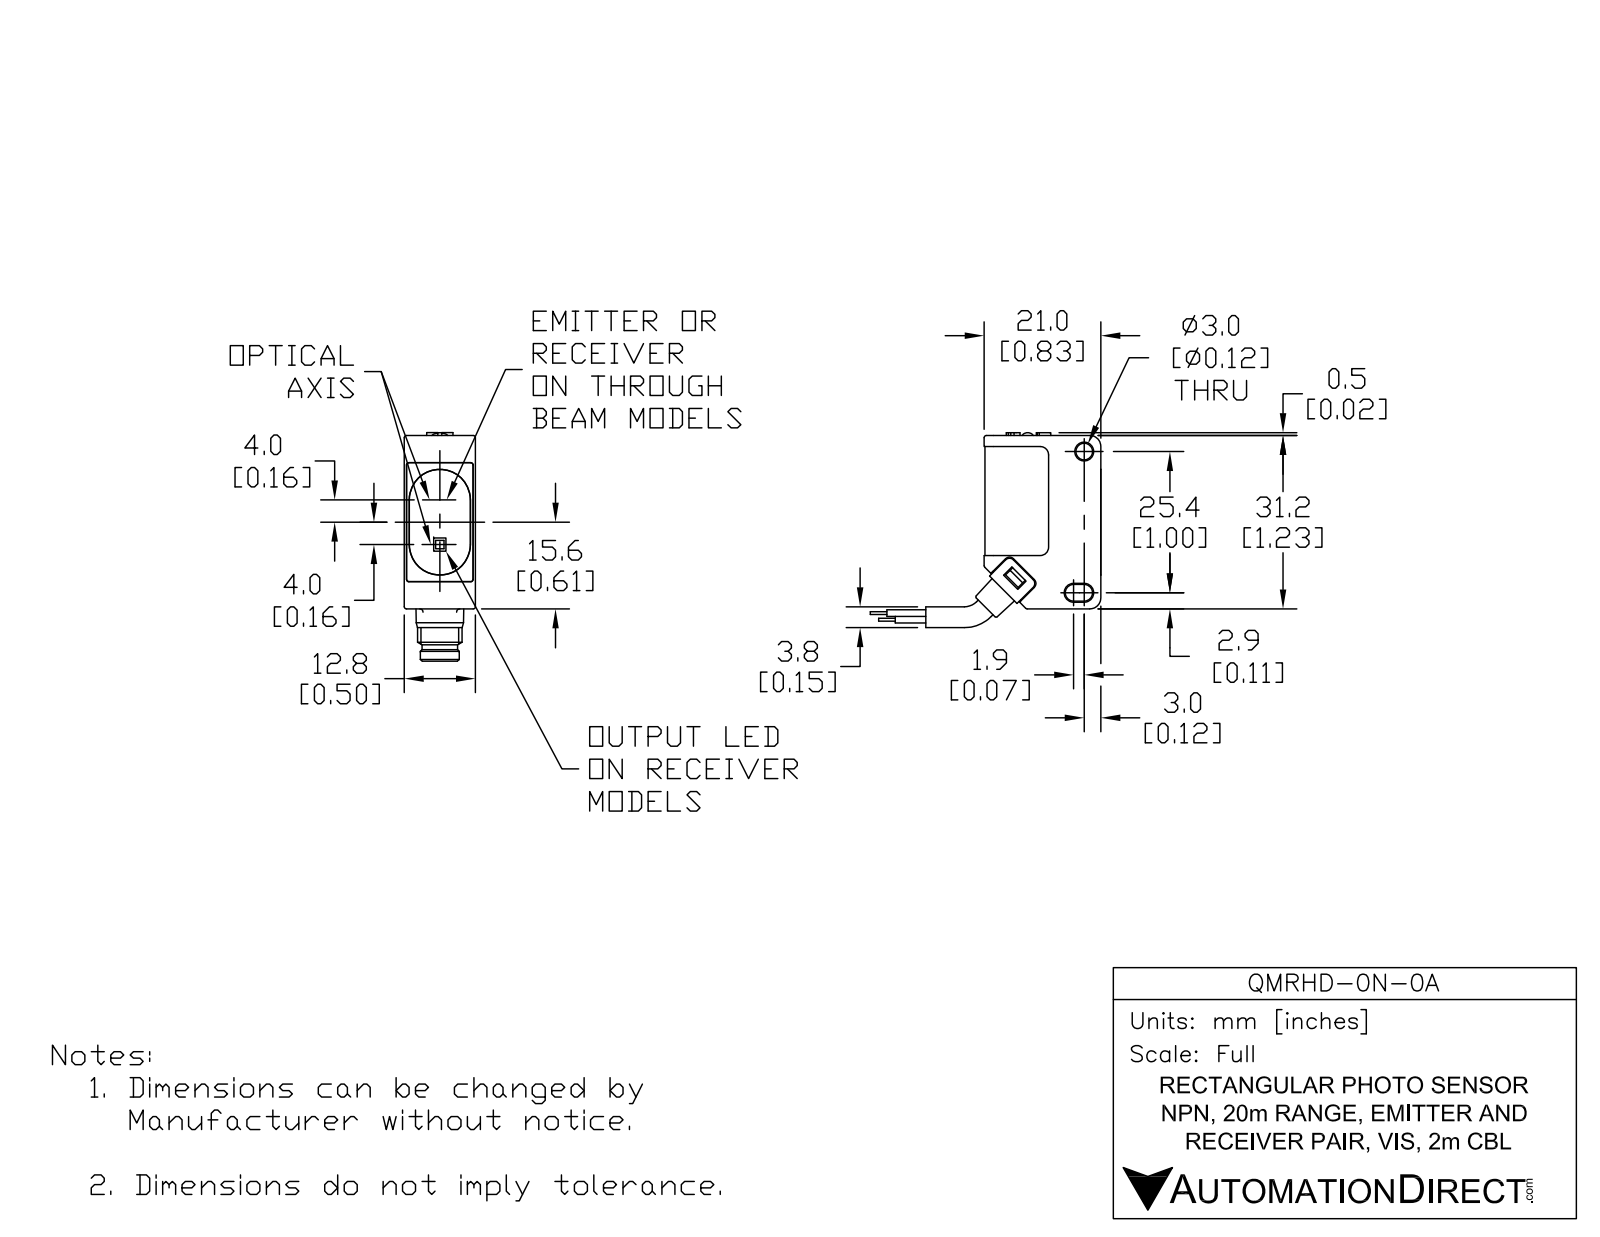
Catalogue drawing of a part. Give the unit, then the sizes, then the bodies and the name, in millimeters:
Units: millimetres
Overall size (bounding box): 81.1 × 26.2 × 13
Round holes (diameter × count): ⌀3 ×3, ⌀3.8 ×1, ⌀5.7 ×1, ⌀7.2 ×1
Round bosses / shafts (diameter × count): ⌀3.5 ×2
Partial cylindrical surfaces — rounded edges, fillets, slot ends (radius × count): R0.4 ×13, R0.5 ×10, R1 ×8, R1.5 ×6, R0.6 ×4, R0.2 ×2, R0.9 ×2, R1.1 ×2
Main face-to-face distances: 0.5, 12.6, 1.5, 0.4, 12.8, 3.5, 12.4, 2, 12.2, 12.5
Hole centre spacings: 5.2
Volume: 7 700 mm³ · Surface area: 5 403 mm²
Bodies: 9 solids, 258 faces (134 planar, 100 cylindrical, 24 other)
Part name (STEP PRODUCT): QMRHD-0N-0A
STEP written by: SolidWorks 2017 (AUTOMOTIVE_DESIGN)
